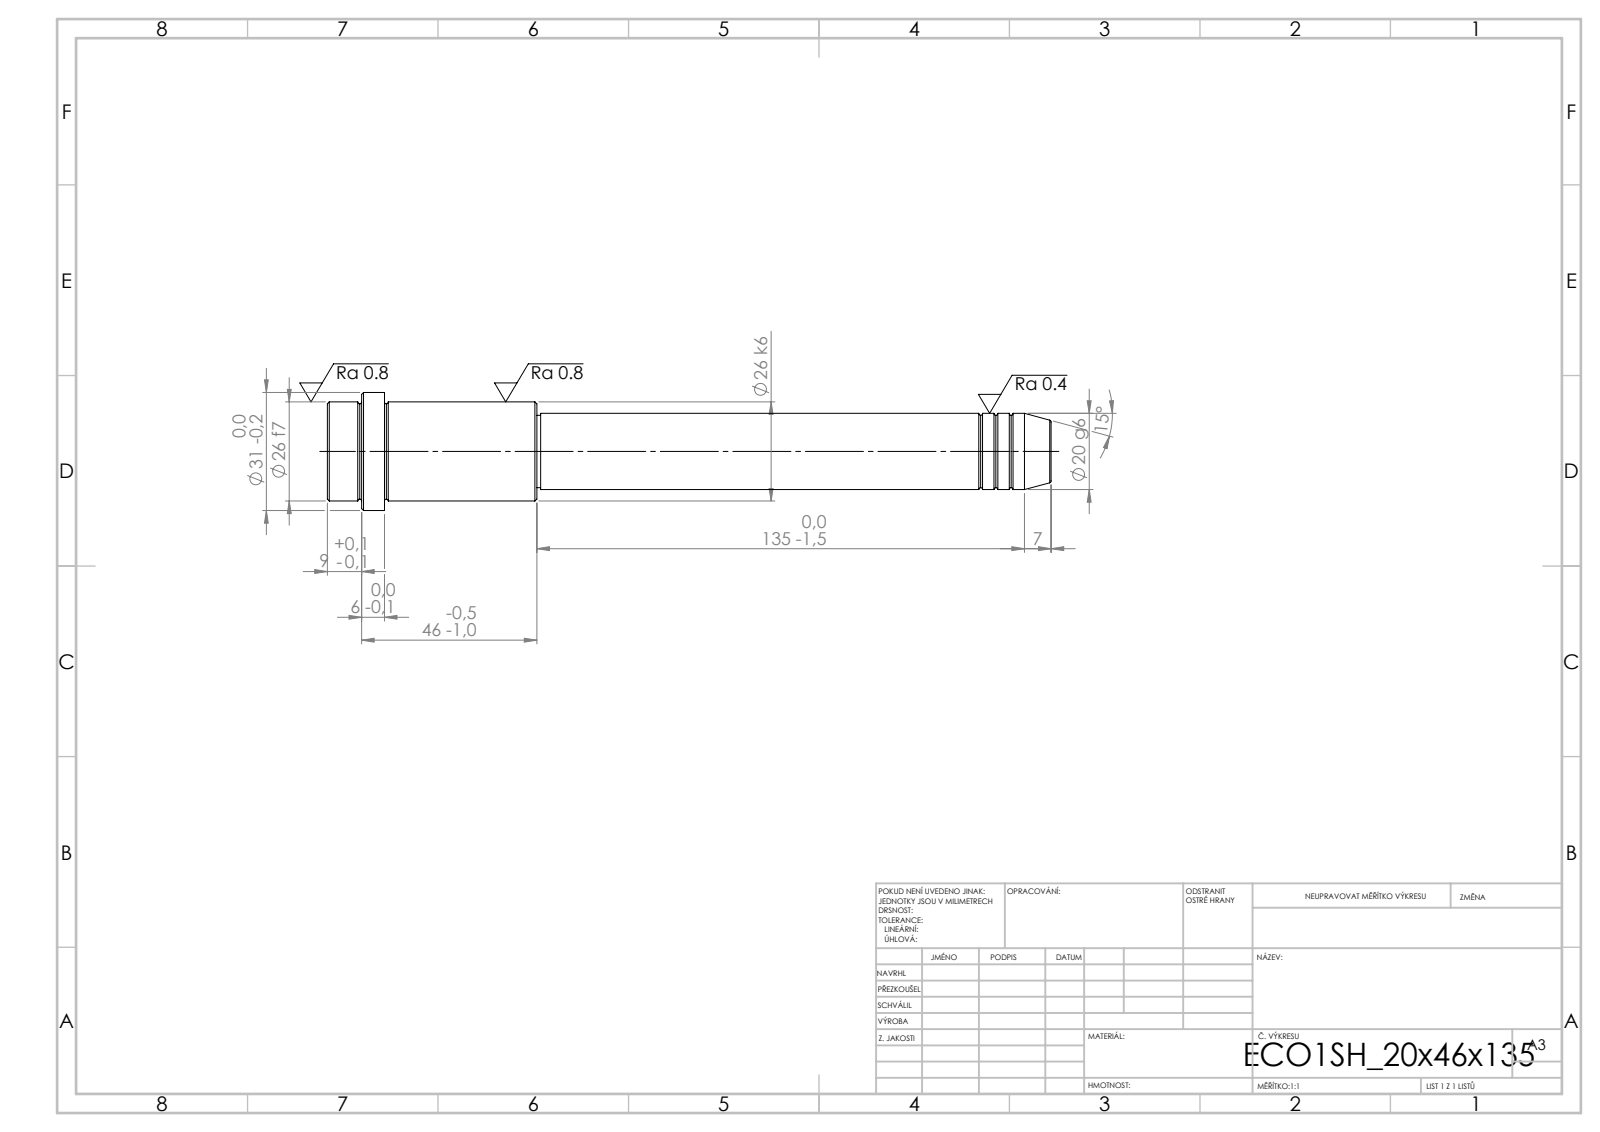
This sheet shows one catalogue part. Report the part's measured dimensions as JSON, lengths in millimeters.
{"step_written_by": "SolidWorks 2019 (CONFIG_CONTROL_DESIGN)", "units": "millimeters", "bodies": {"solids": 1, "faces": 52, "planar": 6, "cylindrical": 16, "other": 30}, "overall_size": [190, 31, 31], "volume_mm3": 72369, "surface_area_mm2": 14605, "round_bosses_or_shafts": [[31, 1], [26, 1], [20, 1], [19, 1]], "face_to_face_distances": [15, 40, 55, 135, 175, 190, 181, 46, 6, 9]}
